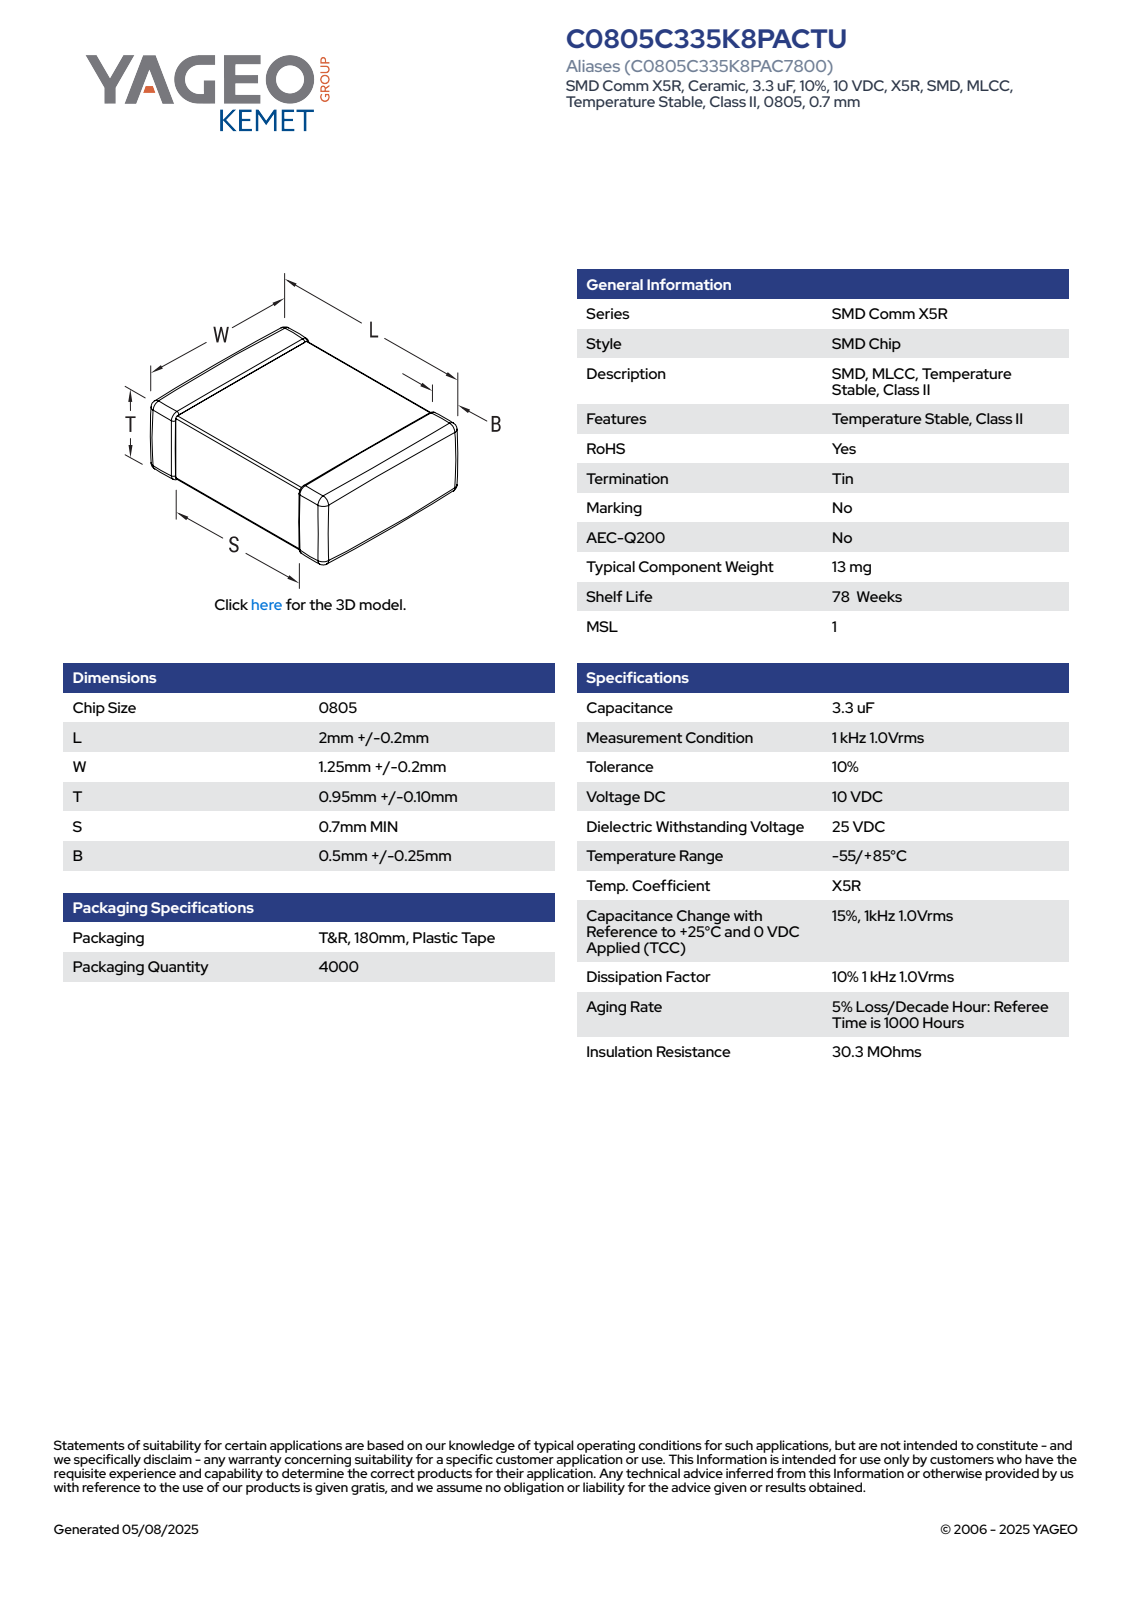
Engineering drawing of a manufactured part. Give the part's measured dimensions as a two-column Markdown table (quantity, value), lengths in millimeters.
| quantity | value |
| --- | --- |
| part name | CCS_CCSTD_0805_L2.2W1.45T1.05B0.5 |
| STEP written by | SolidWorks 2014 (AUTOMOTIVE_DESIGN) |
| units | millimeters |
| bodies | 4 solids, 125 faces (71 planar, 38 cylindrical, 16 other) |
| overall size | 2.2 × 1.45 × 1.05 |
| volume | 3 mm³ |
| surface area | 14 mm² |
| main face-to-face distances | 1.02, 1.42, 0.99, 2.2, 1.05, 1.39, 1.45, 0.97, 1.23, 1.19 |
